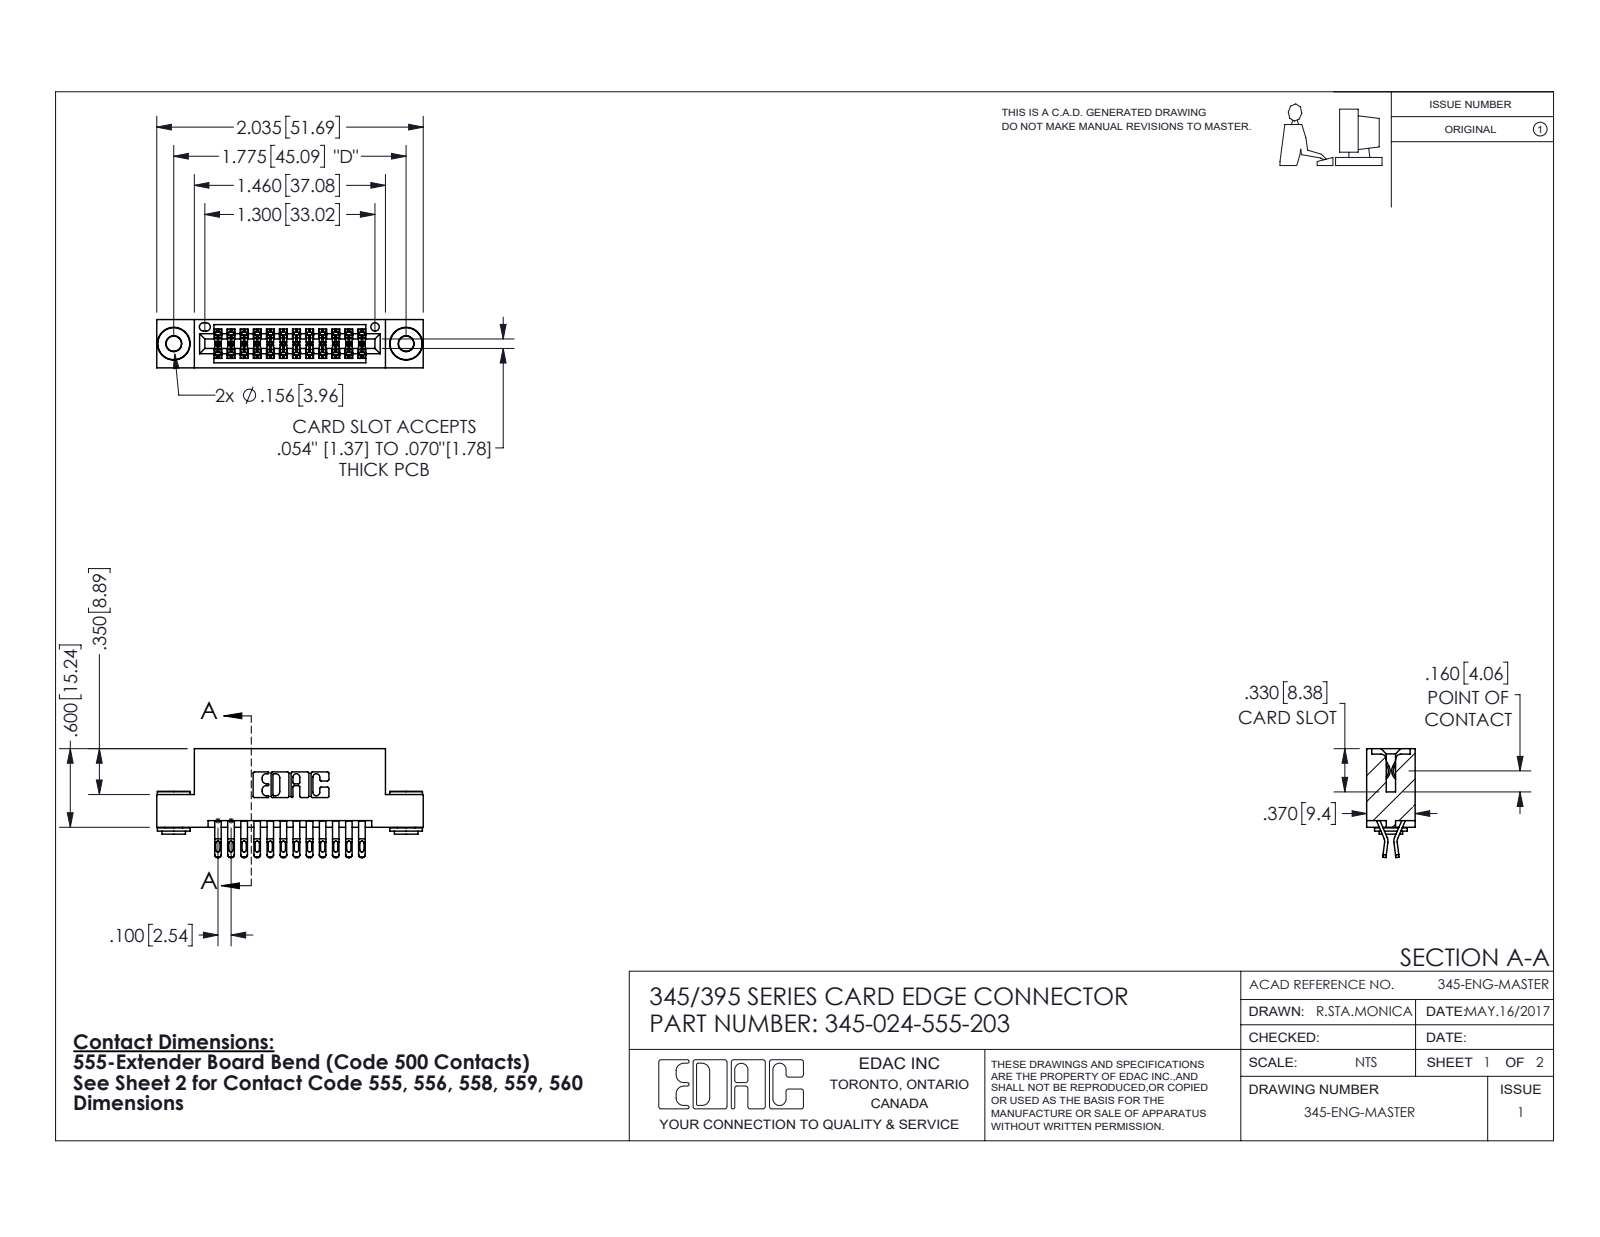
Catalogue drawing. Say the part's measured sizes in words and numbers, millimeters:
The part is named "345 Part_Flush Mounting Lugs - 0.156 Dia-TH; 345-024-555-203; 345-250-002_345-250-002-102; 345-292-001_555 Tail". Its 3-D file was written by "SolidWorks 2016 (CONFIG_CONTROL_DESIGN)". It is 27 solids with 1508 faces: 834 planar, 666 cylindrical and 8 other. Overall it measures 51.7 by 21.1 by 9.4 millimeters. Its volume is 4 830 cubic millimeters and its surface area 7 006 square millimeters. Round holes: 2 of diameter 2.9, 2 of diameter 4, 1 of diameter 1.6. Round bosses or shafts: 2 of diameter 6.4, 2 of diameter 4.6, 2 of diameter 3.5. Partial cylindrical surfaces (rounded edges, fillets, slot ends): 60 of radius 0.4, 48 of radius 0.5, 36 of radius 0.2, 22 of radius 0.3, 6 of radius 0.2, 6 of radius 0.8, 3 of radius 0.7, 2 of radius 0.3. The main face-to-face distances are 5.1, 1.8, 7.6, 9.4, 0.6, 2.5, 6.9, 5.7, 2.5, 7.6. The hole center spacings are 6.9, 39.2, 45.1.
